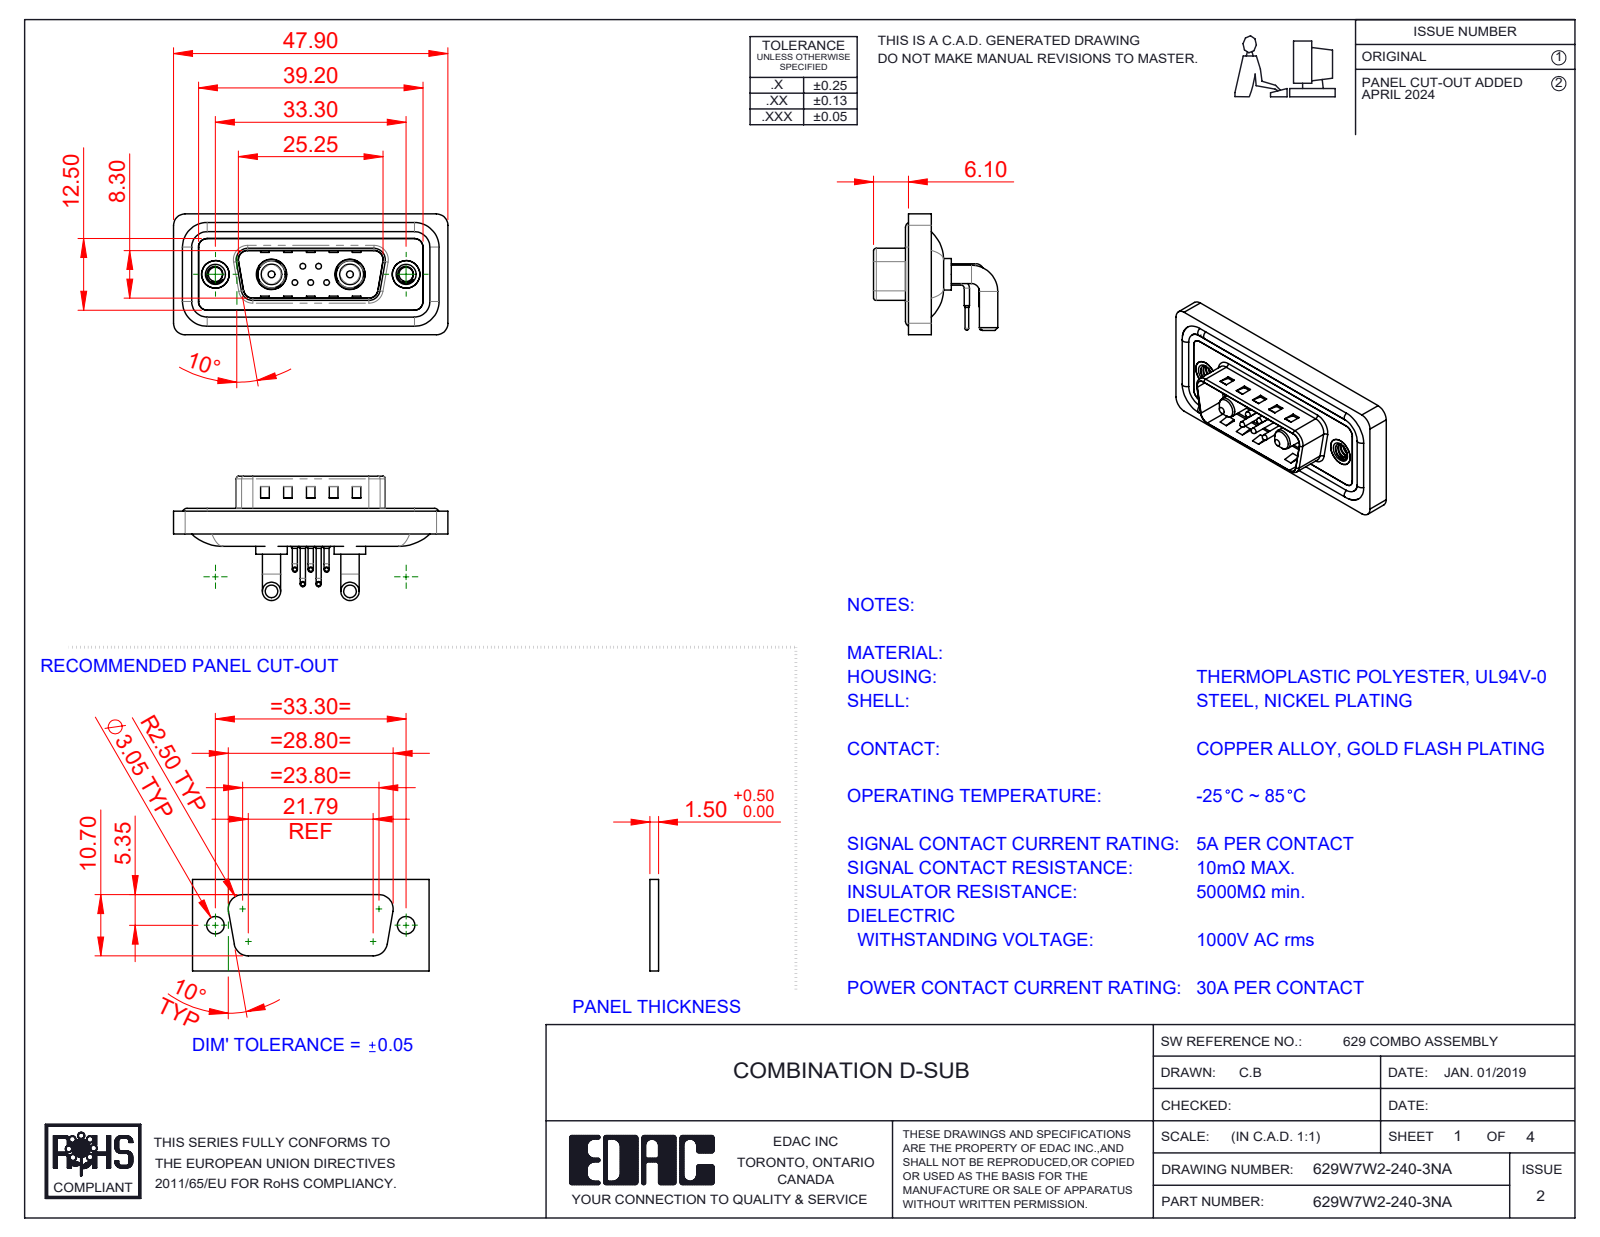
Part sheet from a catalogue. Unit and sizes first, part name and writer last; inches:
Units: inches
Overall size (bounding box): 1.886 × 0.854 × 0.831
Round holes (diameter × count): ⌀0.03 ×5, ⌀0.063 ×5, ⌀0.079 ×5, ⌀0.098 ×2, ⌀0.157 ×2, ⌀0.189 ×2, ⌀0.191 ×2, ⌀0.197 ×2, ⌀0.209 ×2
Round bosses / shafts (diameter × count): ⌀0.035 ×10, ⌀0.059 ×5, ⌀0.039 ×5, ⌀0.026 ×5, ⌀0.126 ×4, ⌀0.063 ×4, ⌀0.217 ×2, ⌀0.205 ×2
Partial cylindrical surfaces — rounded edges, fillets, slot ends (radius × count): R0.079 ×20, R0.059 ×18, R0.02 ×8, R0.063 ×8, R0.04 ×5, R0.01 ×4, R0.024 ×4, R0.026 ×4
Main face-to-face distances: 0.016, 0.114, 0.031, 0.043, 0.083, 0.063, 0.098, 0.122, 0.177, 0.161
Hole centre spacings: 0.124, 0.109, 0.386, 0.925, 0.17, 0.17, 0.198, 0.198
Volume: 0.35 in³ · Surface area: 14.23 in²
Bodies: 16 solids, 1077 faces (517 planar, 404 cylindrical, 156 other)
Part name (STEP PRODUCT): 629Combo Contact Row 1; 629Combo Contact Row 2; Power Pin_30A RA; 629W7W2-140-3NA (+5 more)
STEP written by: SolidWorks 2023 (CONFIG_CONTROL_DESIGN)
